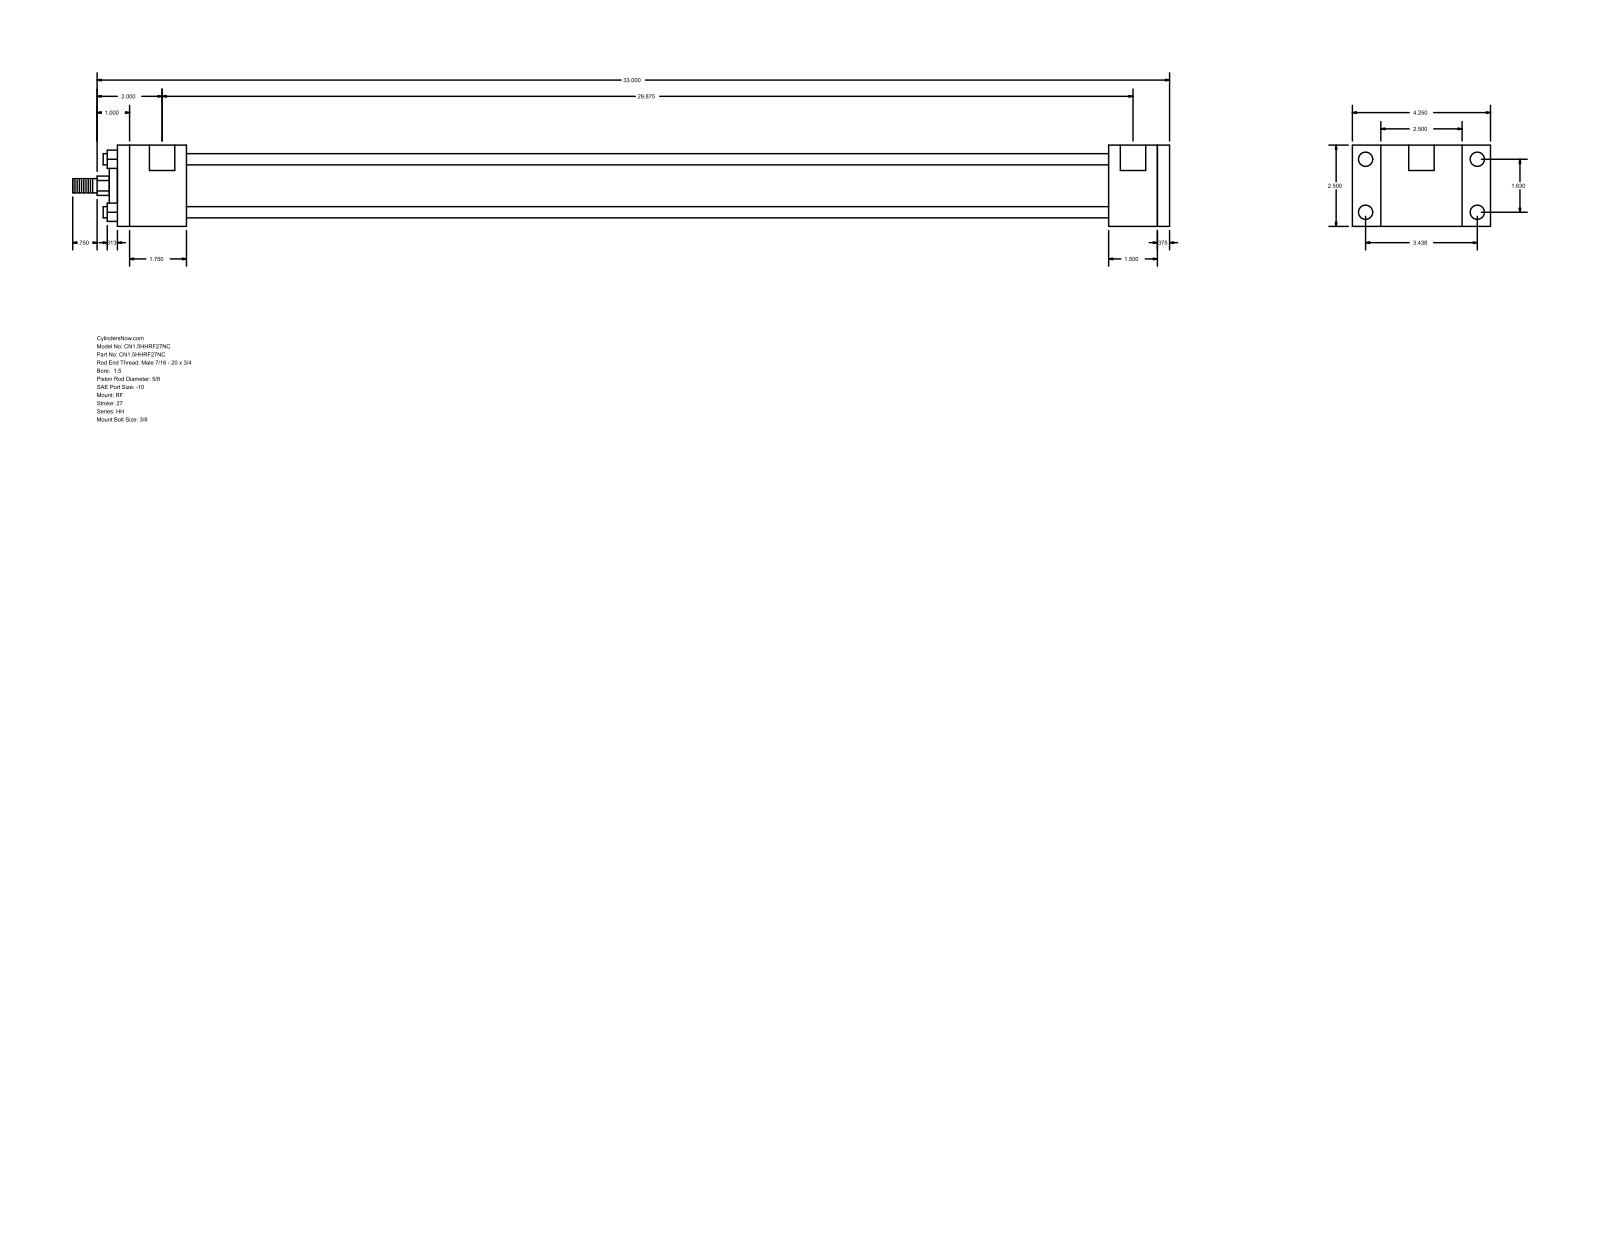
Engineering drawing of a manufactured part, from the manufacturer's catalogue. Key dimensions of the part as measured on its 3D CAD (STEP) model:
Part name (STEP PRODUCT): HH_RF__0150_0.625
STEP written by: GSSL Pune (CONFIG_CONTROL_DESIGN)
Units: millimetres
Bodies: 0 solids, 92 faces (64 planar, 28 cylindrical, 0 other)
Overall size (bounding box): 857.25 × 107.95 × 63.5
Round holes (diameter × count): ⌀5.56 ×4, ⌀11.13 ×4, ⌀19.84 ×2
Round bosses / shafts (diameter × count): ⌀8.76 ×4, ⌀44.45 ×1, ⌀28.57 ×1, ⌀15.88 ×1, ⌀11.11 ×1
Partial cylindrical surfaces — rounded edges, fillets, slot ends (radius × count): R7.54 ×1
Main face-to-face distances: 63.5, 822.32, 9.53, 812.79, 53.97, 774.7, 720.73, 758.82, 768.35, 38.09
Hole centre spacings: 1.59, 41.4, 87.32, 96.64, 760.41, 762, 758.82
